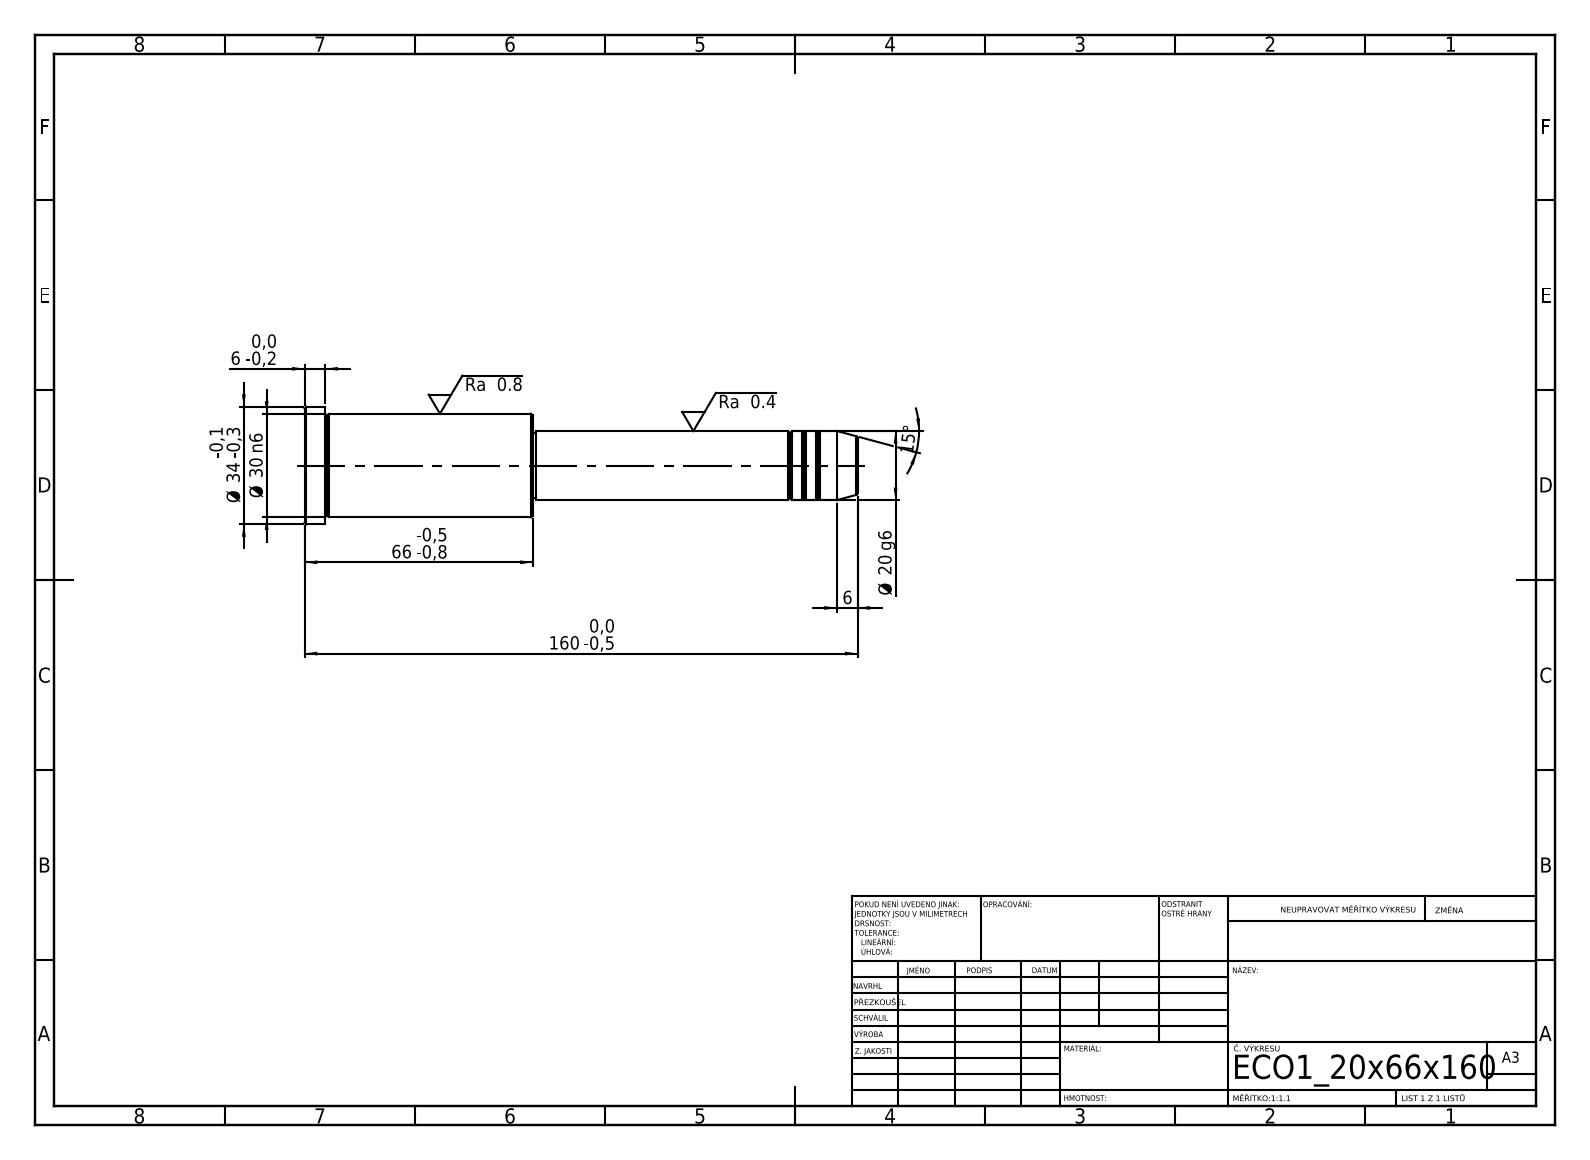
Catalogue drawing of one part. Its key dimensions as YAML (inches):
step_written_by: "SolidWorks 2019 (CONFIG_CONTROL_DESIGN)"
units: inches
bodies: {solids: 1, faces: 43, planar: 5, cylindrical: 14, other: 24}
overall_size: [6.299, 1.339, 1.339]
volume: 4.695
surface_area: 21.77
round_bosses_or_shafts:
  - {diameter: 1.339, count: 1}
  - {diameter: 1.181, count: 1}
  - {diameter: 0.787, count: 1}
  - {diameter: 0.748, count: 1}
face_to_face_distances: [2.598, 3.701, 6.299, 6.063, 2.362, 0.236, 3.661, 0.039, 2.402, 2.638]
